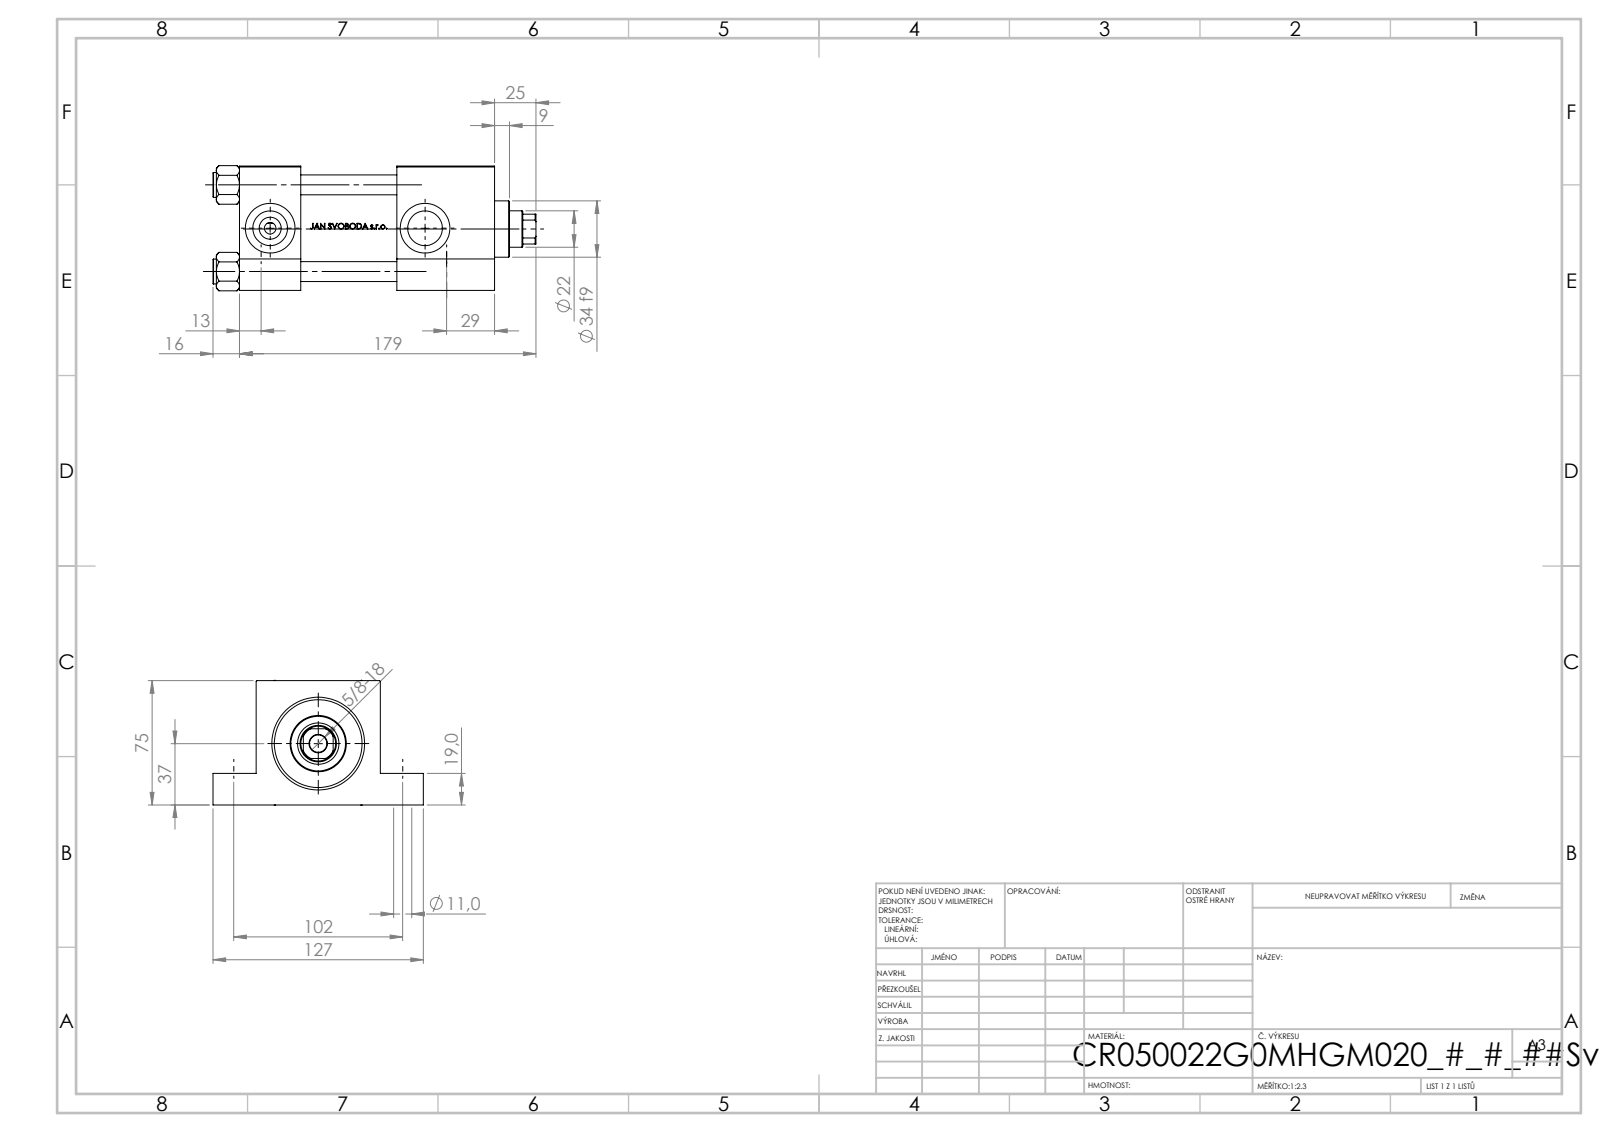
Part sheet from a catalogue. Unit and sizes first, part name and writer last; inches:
Units: inches
Overall size (bounding box): 7.677 × 5 × 2.974
Round holes (diameter × count): ⌀0.472 ×4, ⌀0.433 ×3, ⌀0.276 ×2, ⌀0.825 ×2, ⌀1.181 ×2, ⌀0.413 ×1, ⌀0.433 ×1, ⌀0.866 ×1, ⌀0.984 ×1, ⌀1.614 ×1, ⌀1.969 ×1, ⌀2.087 ×1
Round bosses / shafts (diameter × count): ⌀0.591 ×4, ⌀2.205 ×1, ⌀1.339 ×1
Partial cylindrical surfaces — rounded edges, fillets, slot ends (radius × count): R0.413 ×1
Main face-to-face distances: 2.953, 1.457, 6.063, 4.606, 0.748, 2.205, 3.74, 2.283, 2.323, 1.024
Hole centre spacings: 2.059, 1.442, 1.47, 2.912, 4.016, 4.409, 5.964, 3.681
Volume: 46.12 in³ · Surface area: 247 in²
Bodies: 11 solids, 1087 faces (431 planar, 124 cylindrical, 532 other)
Part name (STEP PRODUCT): V215CR_G_Body; NUT_M5_G; V215CR_VCP_G; V215_VC_A (+1 more)
STEP written by: SolidWorks 2019 (CONFIG_CONTROL_DESIGN)
